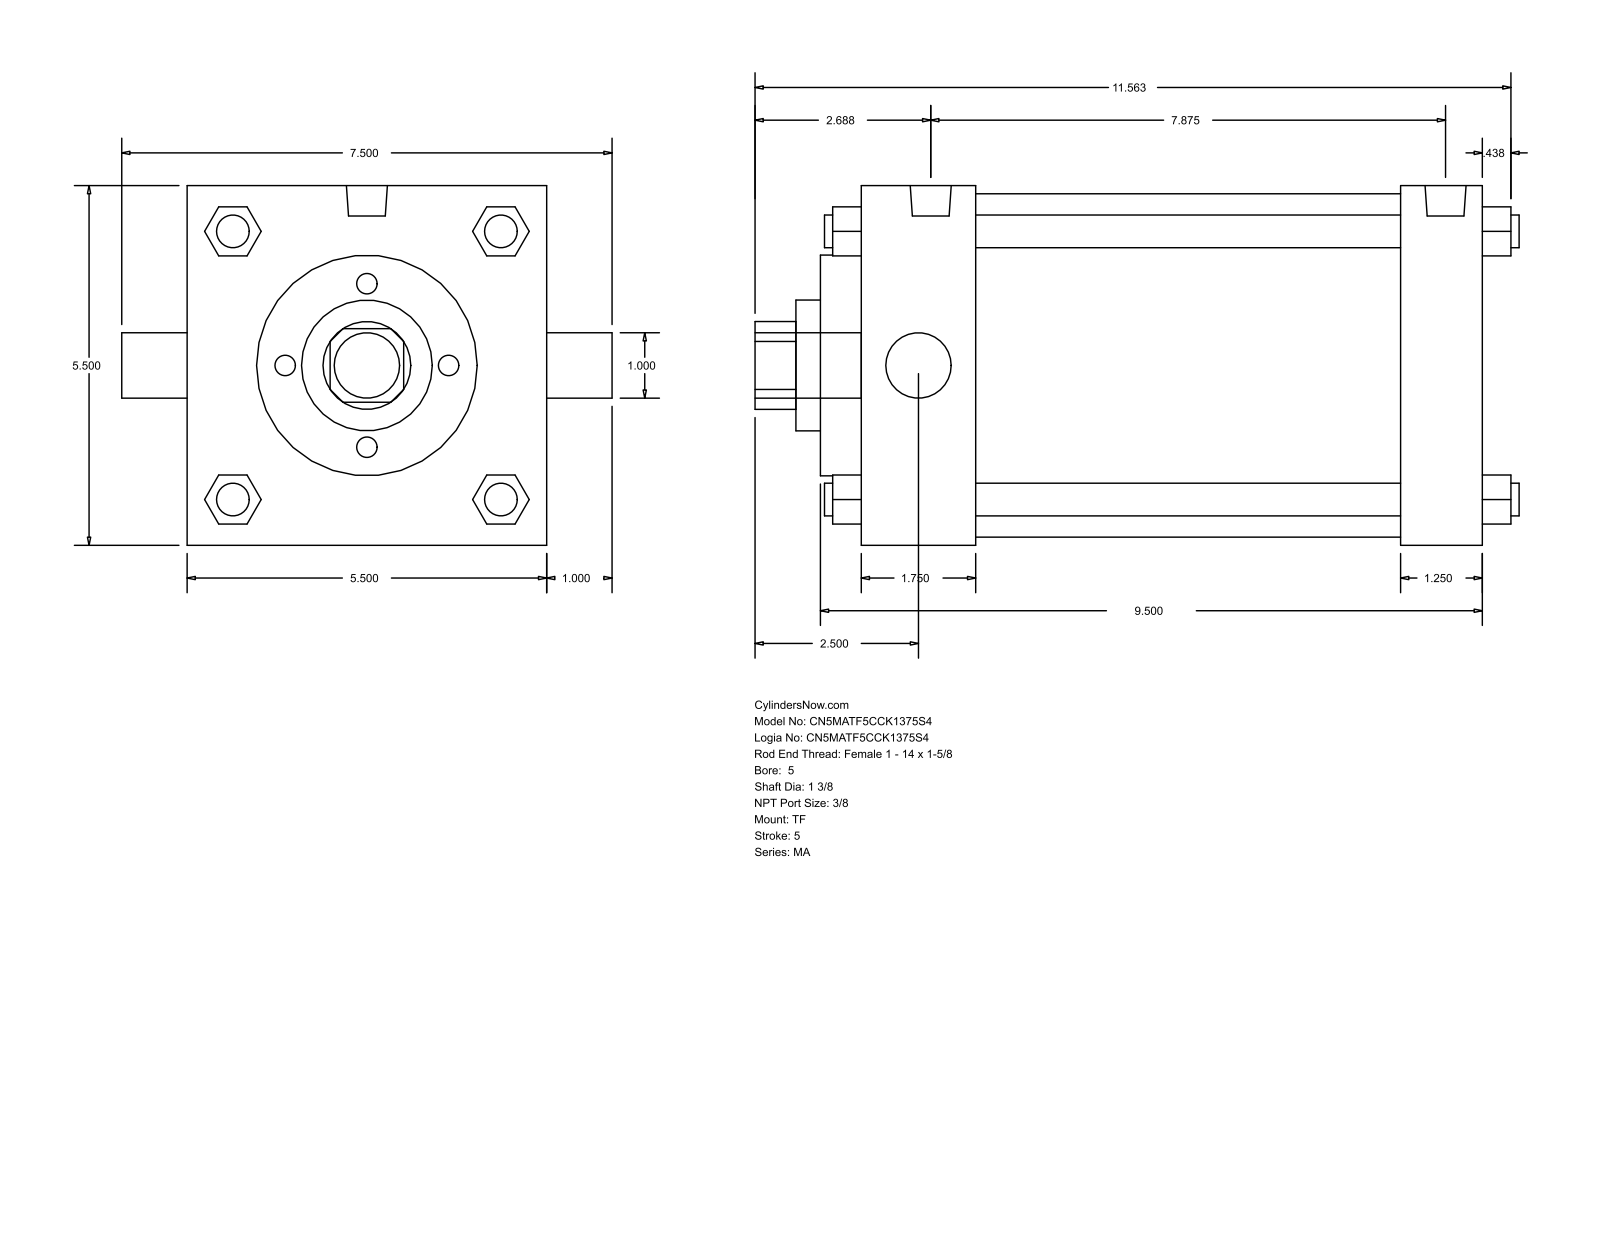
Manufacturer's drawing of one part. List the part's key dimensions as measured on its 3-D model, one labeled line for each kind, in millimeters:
Part name (STEP PRODUCT): MA_TF__0500_1.375
STEP written by: GSSL Pune (CONFIG_CONTROL_DESIGN)
Units: millimetres
Bodies: 0 solids, 122 faces (93 planar, 29 cylindrical, 0 other)
Overall size (bounding box): 296.86 × 190.5 × 139.7
Round holes (diameter × count): ⌀25.4 ×1, ⌀34.92 ×1, ⌀50.8 ×1, ⌀85.72 ×1, ⌀133.35 ×1
Round bosses / shafts (diameter × count): ⌀12.7 ×4, ⌀11.11 ×3, ⌀15.93 ×2, ⌀25.4 ×1
Partial cylindrical surfaces — rounded edges, fillets, slot ends (radius × count): R17.06 ×1
Main face-to-face distances: 139.7, 241.3, 165.1, 209.55, 31.75, 44.45, 196.85, 15.87, 60.32, 225.42
